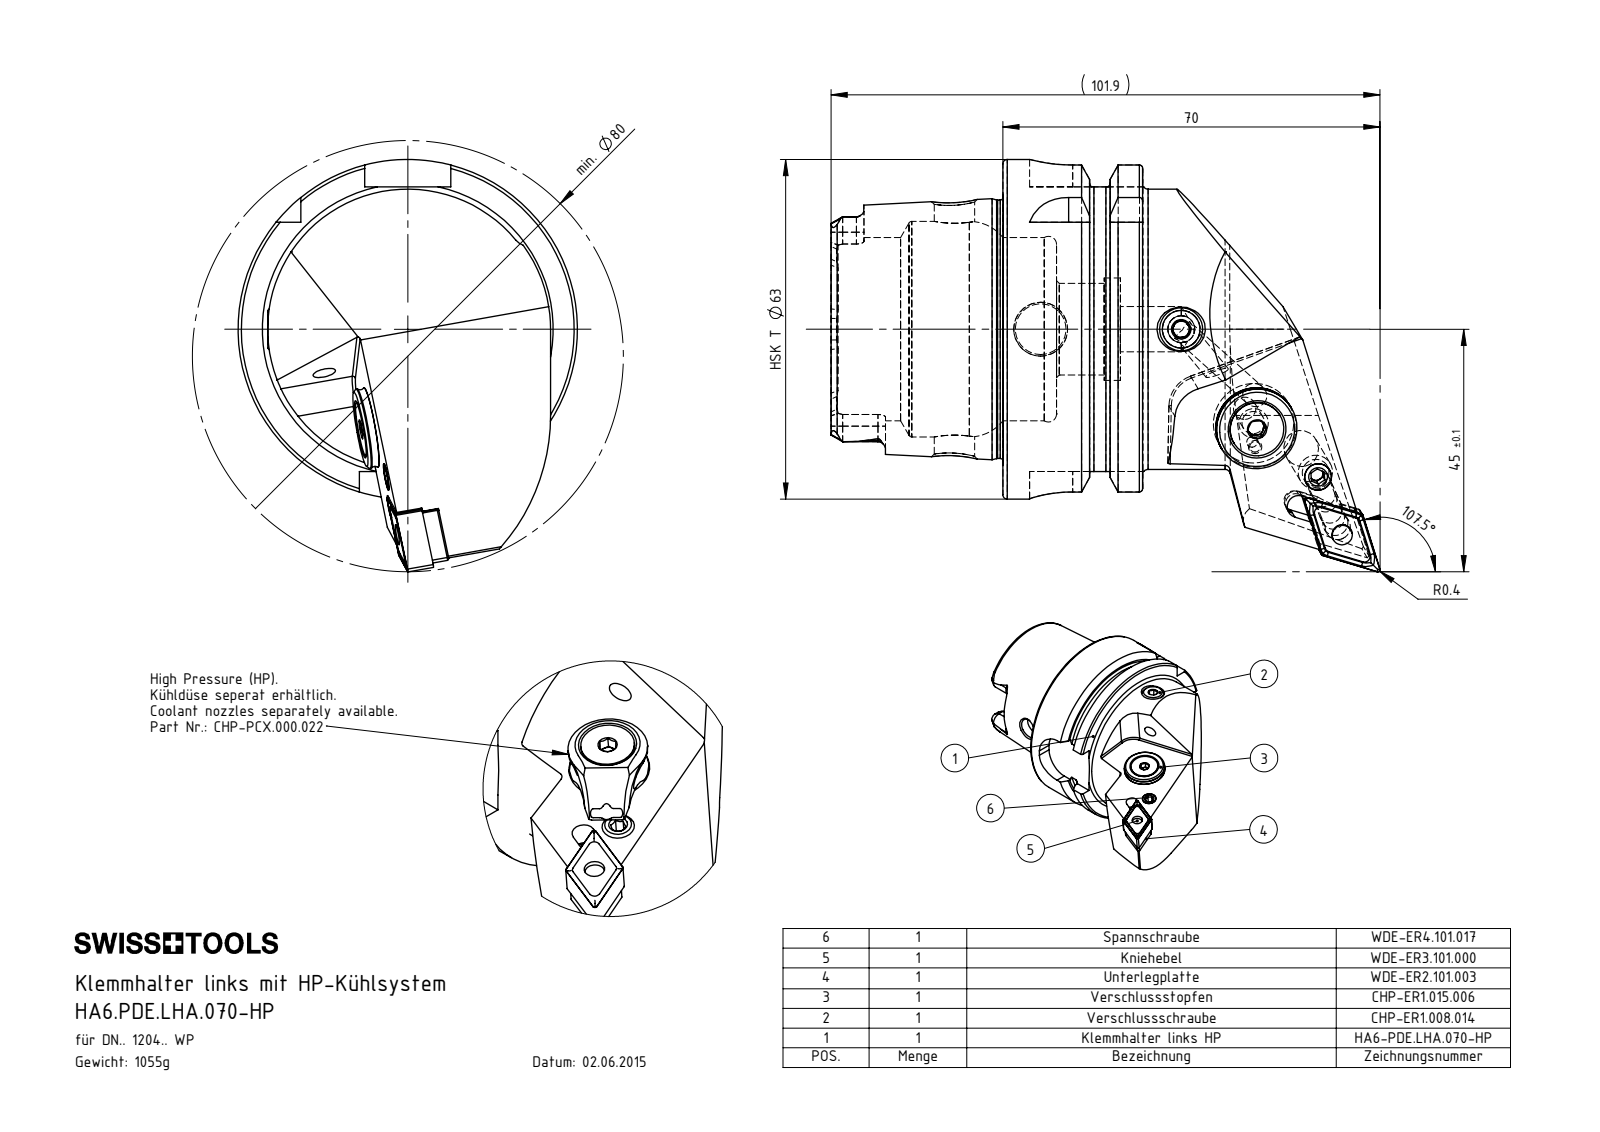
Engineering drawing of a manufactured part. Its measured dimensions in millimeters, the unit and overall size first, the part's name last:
Units: millimetres
Overall size (bounding box): 101.91 × 76.5 × 63
Round holes (diameter × count): ⌀4.2 ×3, ⌀2.5 ×2, ⌀5 ×2, ⌀1.2 ×1, ⌀2 ×1, ⌀3 ×1, ⌀3.81 ×1, ⌀4.8 ×1, ⌀5.2 ×1, ⌀6.4 ×1, ⌀7 ×1, ⌀7.5 ×1
Round bosses / shafts (diameter × count): ⌀63 ×1, ⌀54.95 ×1, ⌀52 ×1, ⌀47.94 ×1, ⌀15 ×1, ⌀13.4 ×1, ⌀10 ×1, ⌀8 ×1
Partial cylindrical surfaces — rounded edges, fillets, slot ends (radius × count): R0.4 ×8, R1.4 ×6, R2.1 ×5, R2.88 ×4, R8 ×4, R0.5 ×2, R1.83 ×1, R1.85 ×1
Main face-to-face distances: 25.95, 16, 9.95, 31.9, 41.85, 57.85, 52.8, 21.8, 11.85, 4.5
Hole centre spacings: 11.8, 4.51, 12.36, 12.37, 15, 15.01, 22.42, 22.43
Volume: 134 625 mm³ · Surface area: 33 556 mm²
Bodies: 11 solids, 396 faces (175 planar, 85 cylindrical, 136 other)
Part name (STEP PRODUCT): WDE-ER1.101.000; CHP-ER1.015.006; ISO 8752 2x8; WDE-ER4.101.017_A (+8 more)
STEP written by: SolidWorks 2017 (AUTOMOTIVE_DESIGN)
